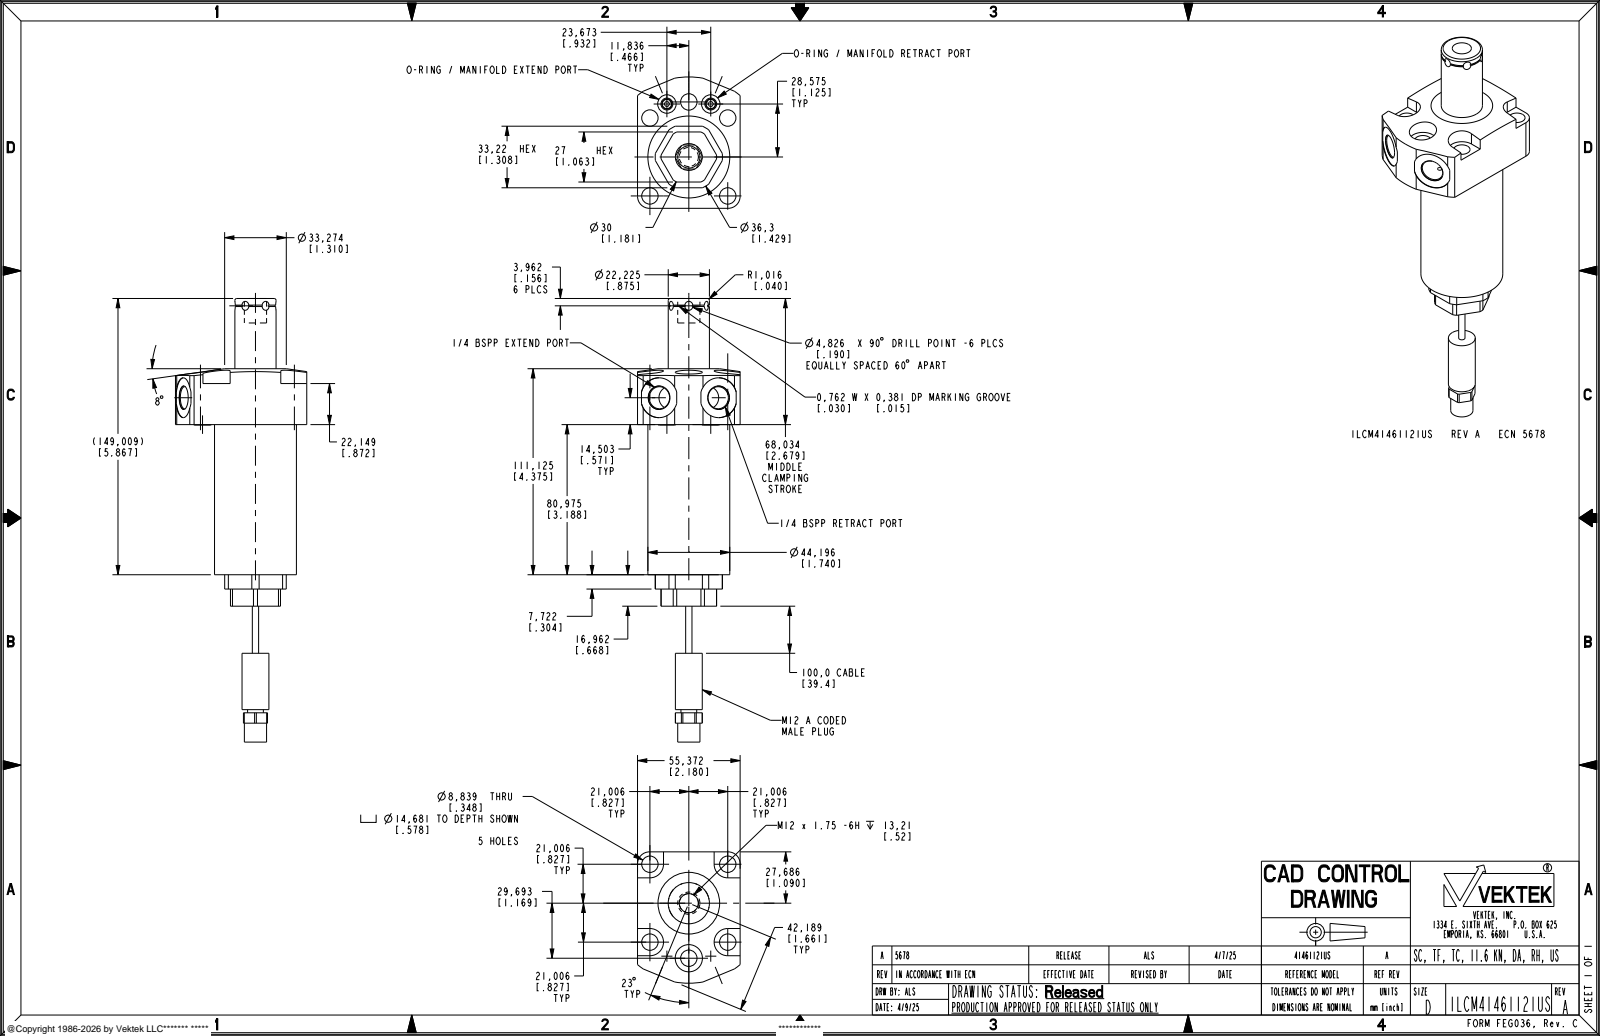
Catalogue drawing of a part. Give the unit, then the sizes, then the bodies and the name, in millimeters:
Units: millimetres
Overall size (bounding box): 239.28 × 77.22 × 60.45
Round holes (diameter × count): ⌀8.84 ×5, ⌀2.49 ×2, ⌀6.5 ×2, ⌀9.96 ×2, ⌀11.89 ×2, ⌀21.5 ×2, ⌀10.31 ×1, ⌀14.68 ×1
Round bosses / shafts (diameter × count): ⌀5.49 ×2, ⌀44.2 ×1, ⌀22.23 ×1, ⌀14.5 ×1, ⌀11.99 ×1, ⌀11.99 ×1, ⌀8.51 ×1, ⌀3.4 ×1
Partial cylindrical surfaces — rounded edges, fillets, slot ends (radius × count): R7.34 ×4, R6.48 ×2, R10.73 ×1, R15 ×1, R18.15 ×1, R43.18 ×1
Main face-to-face distances: 55.38, 3.11, 30.11, 97.94, 16.97, 80.97, 120.09, 103.12, 22.15, 128.09
Hole centre spacings: 29.71, 42.02, 11.88, 11.89, 22.73, 30.93, 33.71, 50.42
Volume: 249 203 mm³ · Surface area: 38 183 mm²
Bodies: 1 solid, 211 faces (90 planar, 87 cylindrical, 34 other)
Part name (STEP PRODUCT): ILCM41461121US
STEP written by: CREO PARAMETRIC BY PTC INC, 2021164 (AUTOMOTIVE_DESIGN)
